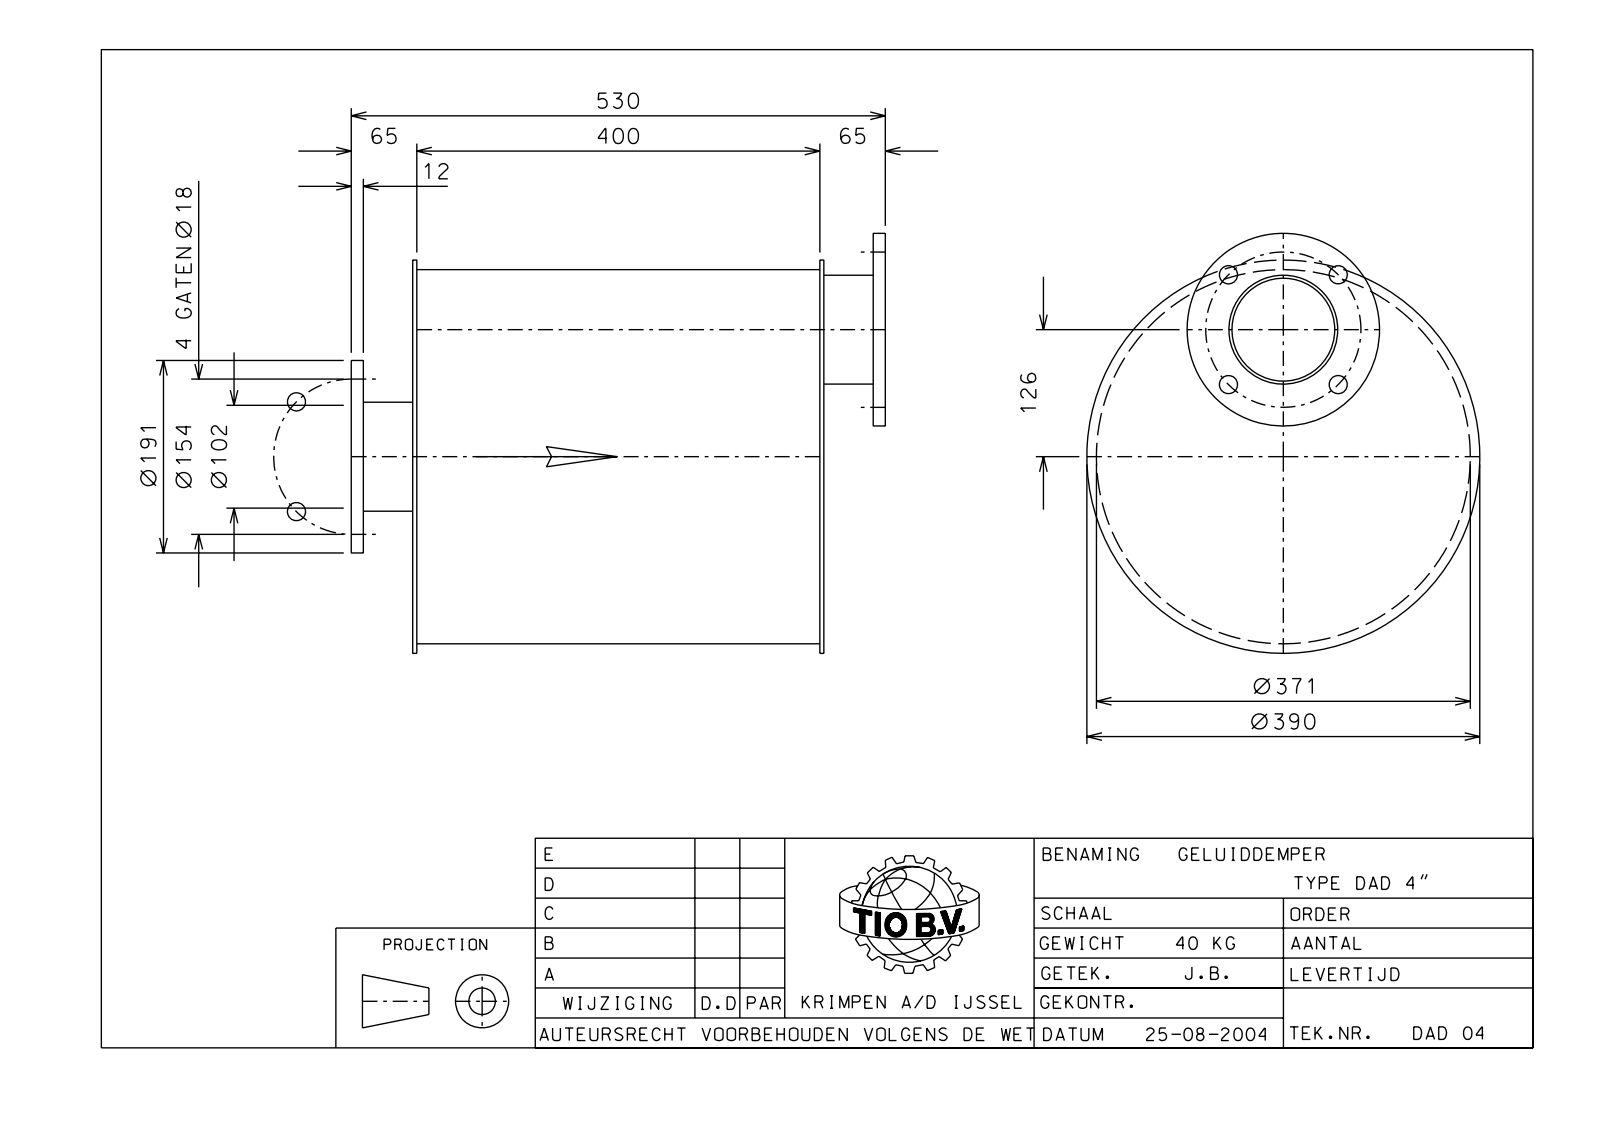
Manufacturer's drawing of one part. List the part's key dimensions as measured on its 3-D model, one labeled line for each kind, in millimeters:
Part name (STEP PRODUCT): MAAT3D
STEP written by: Autodesk Inventor 2015 (AUTOMOTIVE_DESIGN)
Units: millimetres
Bodies: 9 solids, 44 faces (18 planar, 26 cylindrical, 0 other)
Overall size (bounding box): 530 × 417.5 × 390
Volume: 3 878 000 mm³ · Surface area: 2 159 000 mm²
Round holes (diameter × count): ⌀18 ×8, ⌀107.1 ×2, ⌀116 ×2, ⌀116.3 ×2, ⌀364 ×1
Round bosses / shafts (diameter × count): ⌀191 ×2, ⌀114.3 ×2, ⌀390 ×1, ⌀370 ×1
Main face-to-face distances: 4, 404, 400, 408, 61, 65, 465, 469, 518, 49
Hole centre spacings: 77, 108.9, 127, 90.71, 154.01, 167.3, 189.44, 18.1
